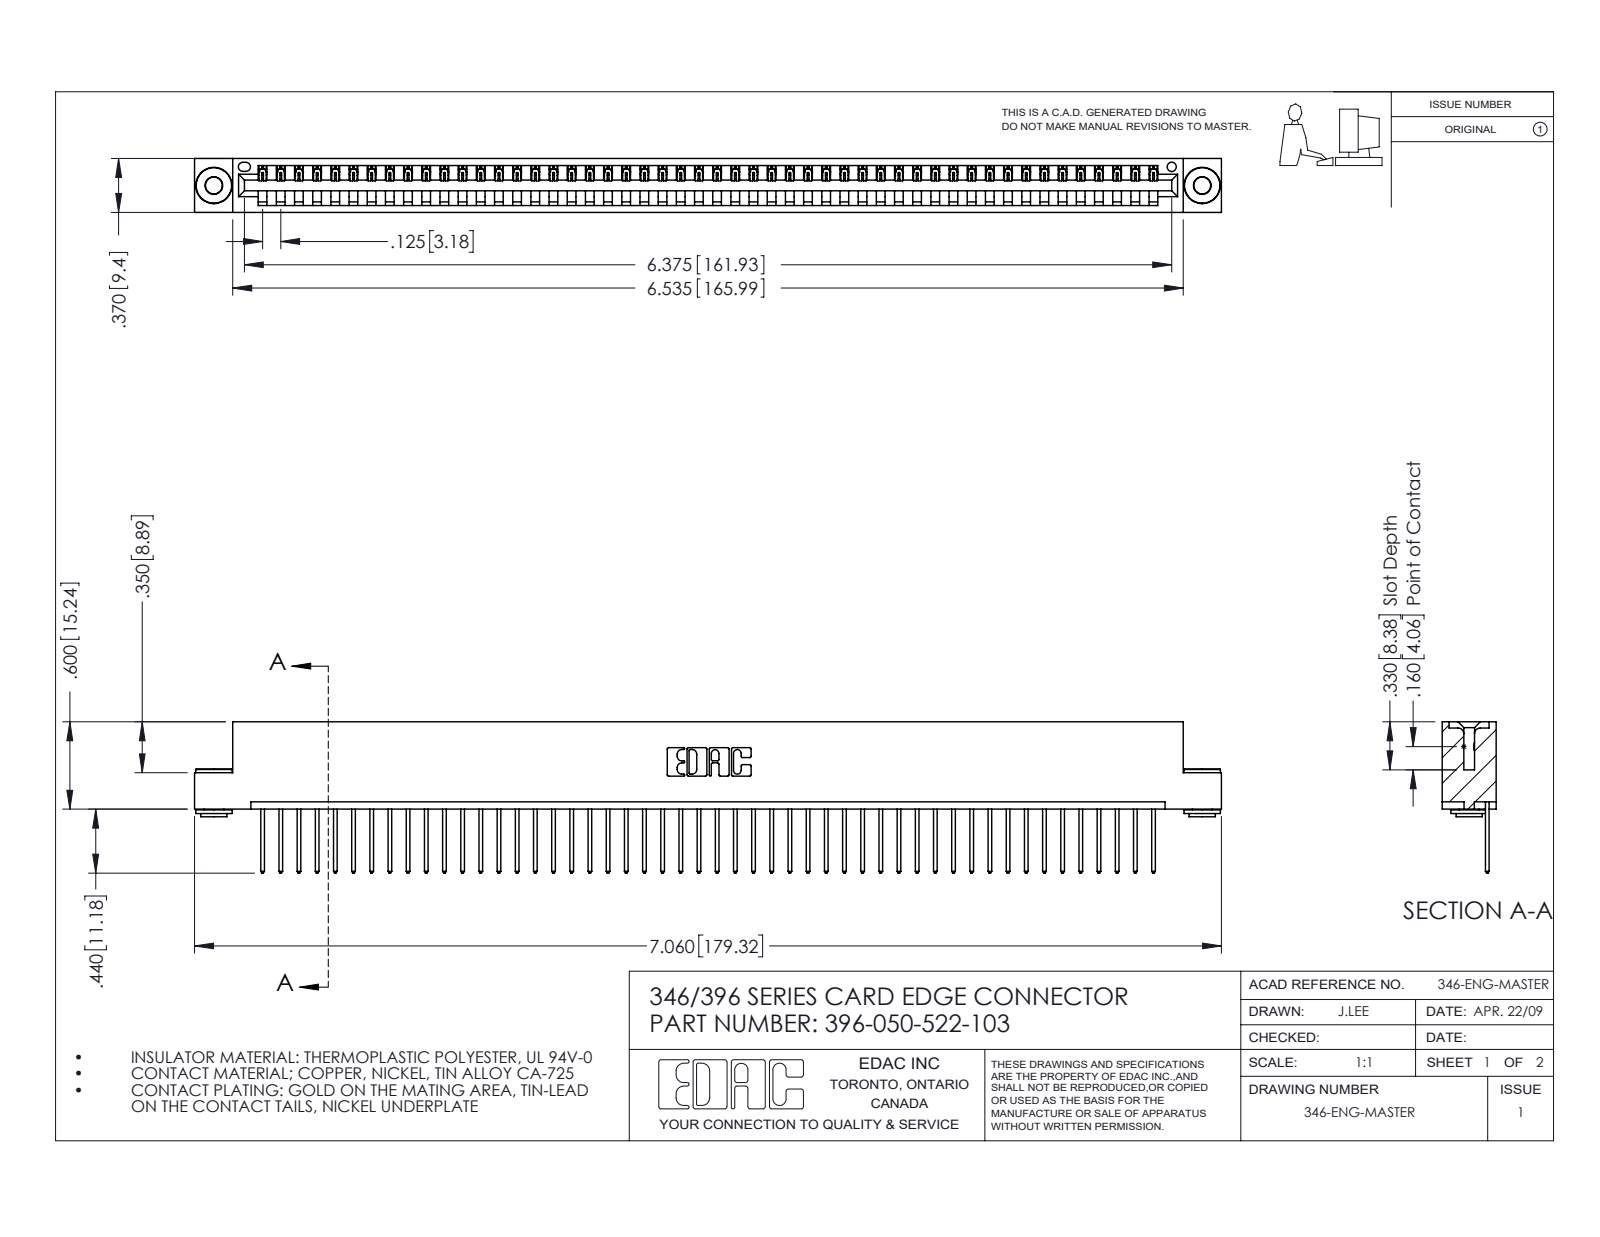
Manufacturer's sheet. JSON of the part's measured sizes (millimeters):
{"part_name": "345-292-001_345-293-122; 345-250-002_345-250-002-102; 346 Part_Flush Mounting Lugs - 0.156 Dia-TH; 396-050-522-103", "step_written_by": "SolidWorks 2016 (CONFIG_CONTROL_DESIGN)", "units": "millimeters", "bodies": {"solids": 53, "faces": 3060, "planar": 2086, "cylindrical": 966, "other": 8}, "overall_size": [179.3, 26.4, 9.4], "volume_mm3": 17240, "surface_area_mm2": 22050, "round_holes": [[2.9, 2], [4, 2], [1.6, 1]], "round_bosses_or_shafts": [[6.4, 2], [4.6, 2], [3.5, 2]], "partial_cylinders_radius": [[0.2, 100], [0.3, 100], [0.3, 22], [0.2, 6], [0.8, 6], [0.7, 3], [0.8, 2], [1, 2]], "face_to_face_distances": [1.2, 8.2, 9.4, 6.4, 0.6, 1.8, 7.6, 3.8, 5.6, 2.5], "hole_center_spacings": [6.2, 167.3, 172.6]}
